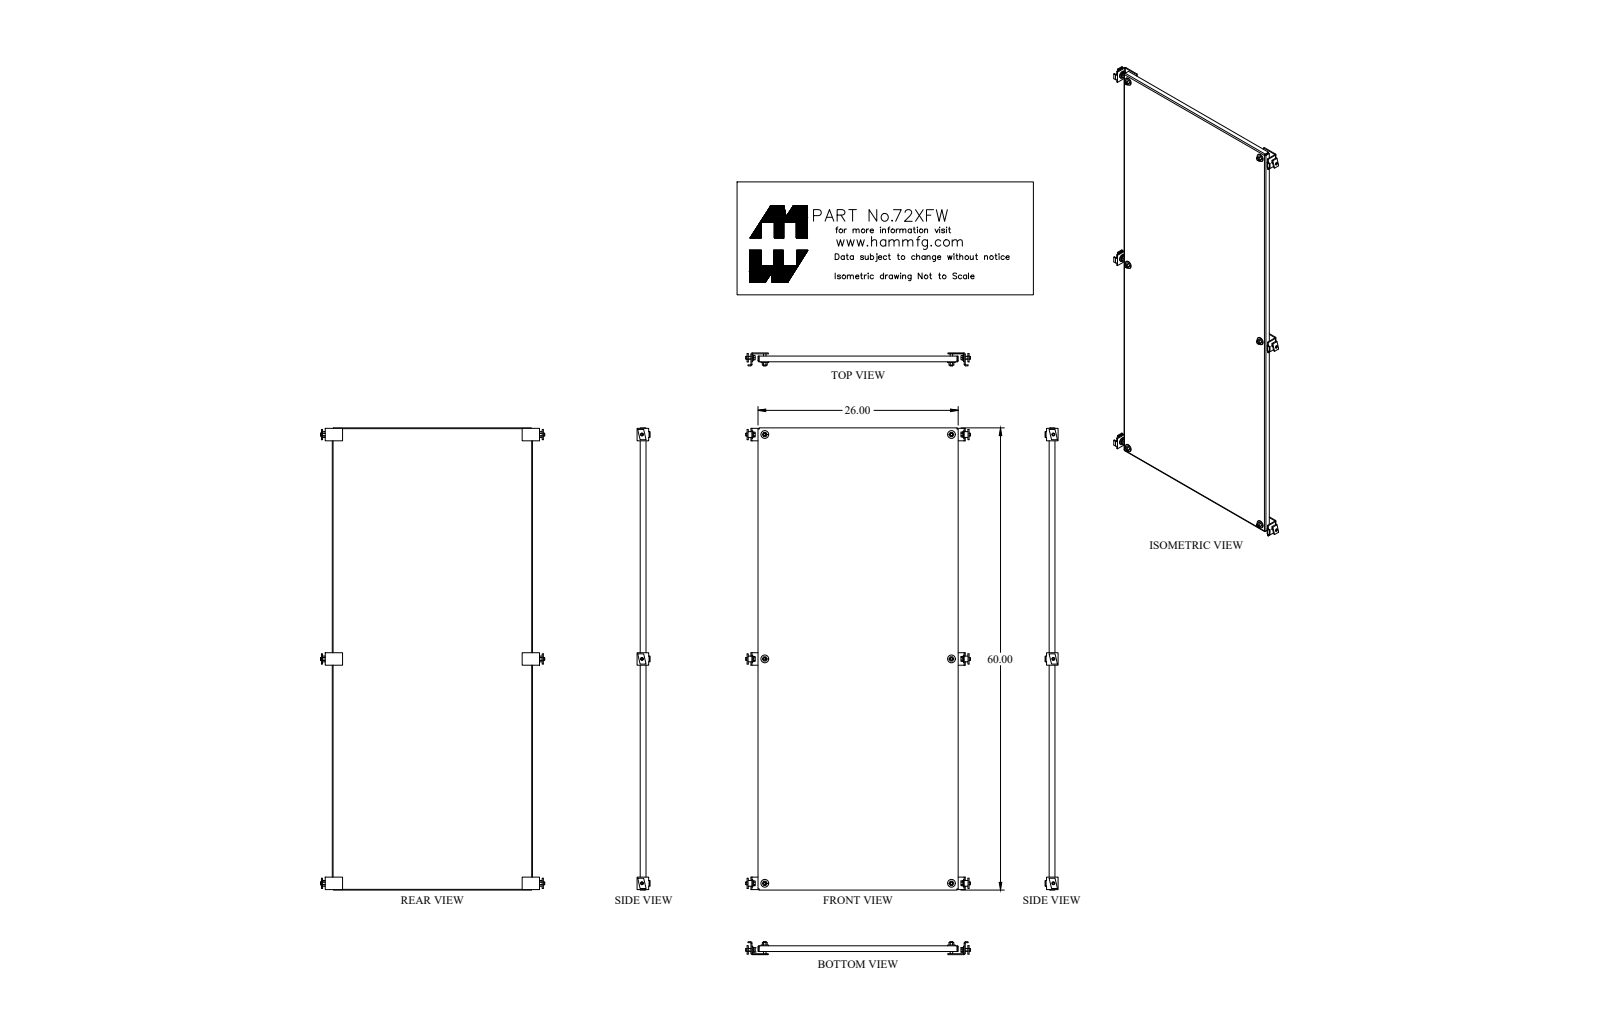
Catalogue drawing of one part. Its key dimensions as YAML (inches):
part_name: "72XFW_Default"
step_written_by: "SolidWorks 2018 (CONFIG_CONTROL_DESIGN)"
units: inches
bodies: {solids: 1, faces: 42, planar: 22, cylindrical: 20, other: 0}
overall_size: [60, 26, 0.75]
volume: 158
surface_area: 3344
round_holes:
  - {diameter: 0.563, count: 6}
partial_cylinders:
  - {radius: 0.048, count: 4}
  - {radius: 0.143, count: 4}
face_to_face_distances: [0.095, 25.905, 25.81, 26, 59.905, 0.75, 0.655, 60, 59.81, 0.143]
hole_center_spacings: [29.125, 37.899, 24.25, 58.25, 63.096]
